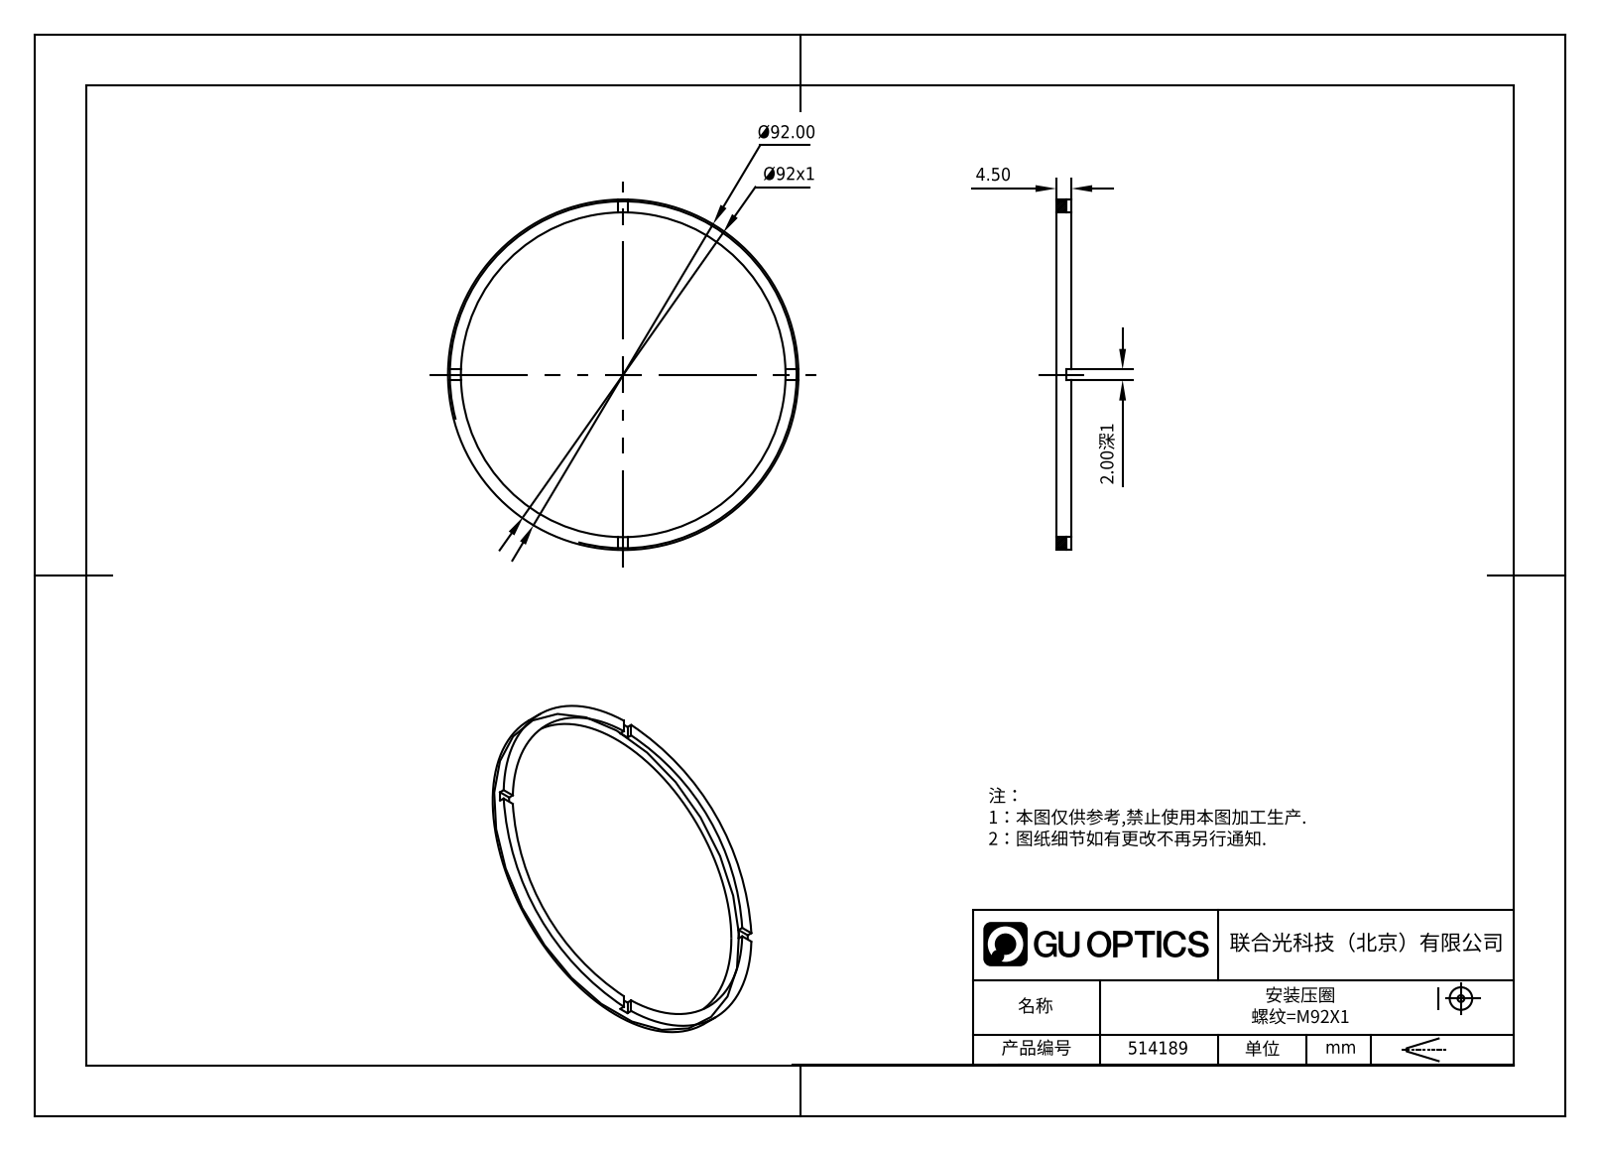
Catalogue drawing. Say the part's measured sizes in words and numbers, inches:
The part is named "514189". Its 3-D file was written by "SolidWorks 2020 (CONFIG_CONTROL_DESIGN)". It is 1 solid with 21 faces: 17 planar, 4 cylindrical and 0 other. Overall it measures 3.622 by 3.622 by 0.177 inches. Its volume is 0.266 cubic inches and its surface area 6.913 square inches. Round holes: 1 of diameter 3.346. Round bosses or shafts: 1 of diameter 3.622. The main face-to-face distances are 0.177, 0.138, 0.039, 0.079.
